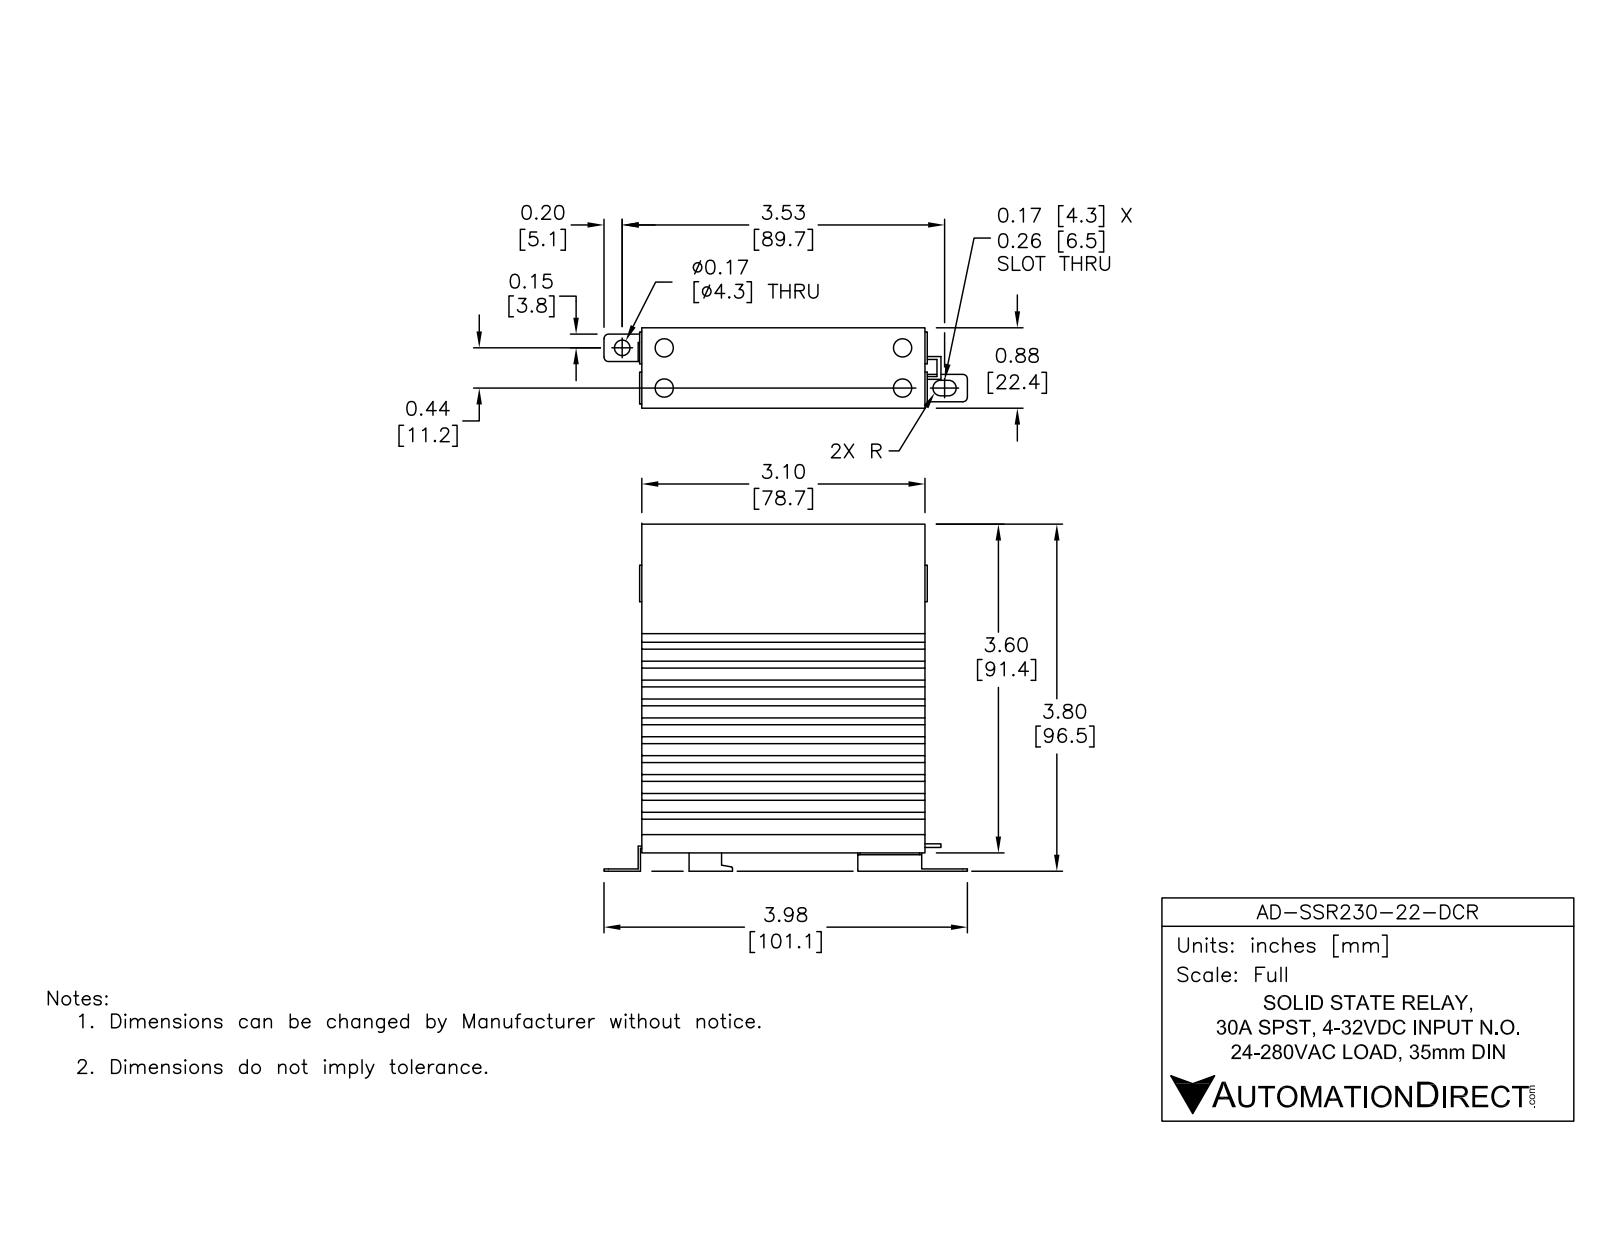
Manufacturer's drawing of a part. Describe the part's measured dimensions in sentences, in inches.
The part is named "AD-SSR230-22-DCR". Its 3-D file was written by "SolidWorks 2014 (AUTOMOTIVE_DESIGN)". It is 1 solid with 215 faces: 195 planar, 20 cylindrical and 0 other. Overall it measures 3.98 by 3.8 by 0.88 inches. Its volume is 7.136 cubic inches and its surface area 74.91 square inches. Round holes: 4 of diameter 0.2, 1 of diameter 0.17. Partial cylindrical surfaces (rounded edges, fillets, slot ends): 6 of radius 0.05, 2 of radius 0.085, 1 of radius 0.015. The main face-to-face distances are 0.62, 0.207, 0.827, 0.414, 0.132, 0.489, 0.339, 0.413, 0.075, 0.207. The hole center spacings are 0.44, 2.61, 2.647, 0.46, 0.637, 3.07, 3.102.
